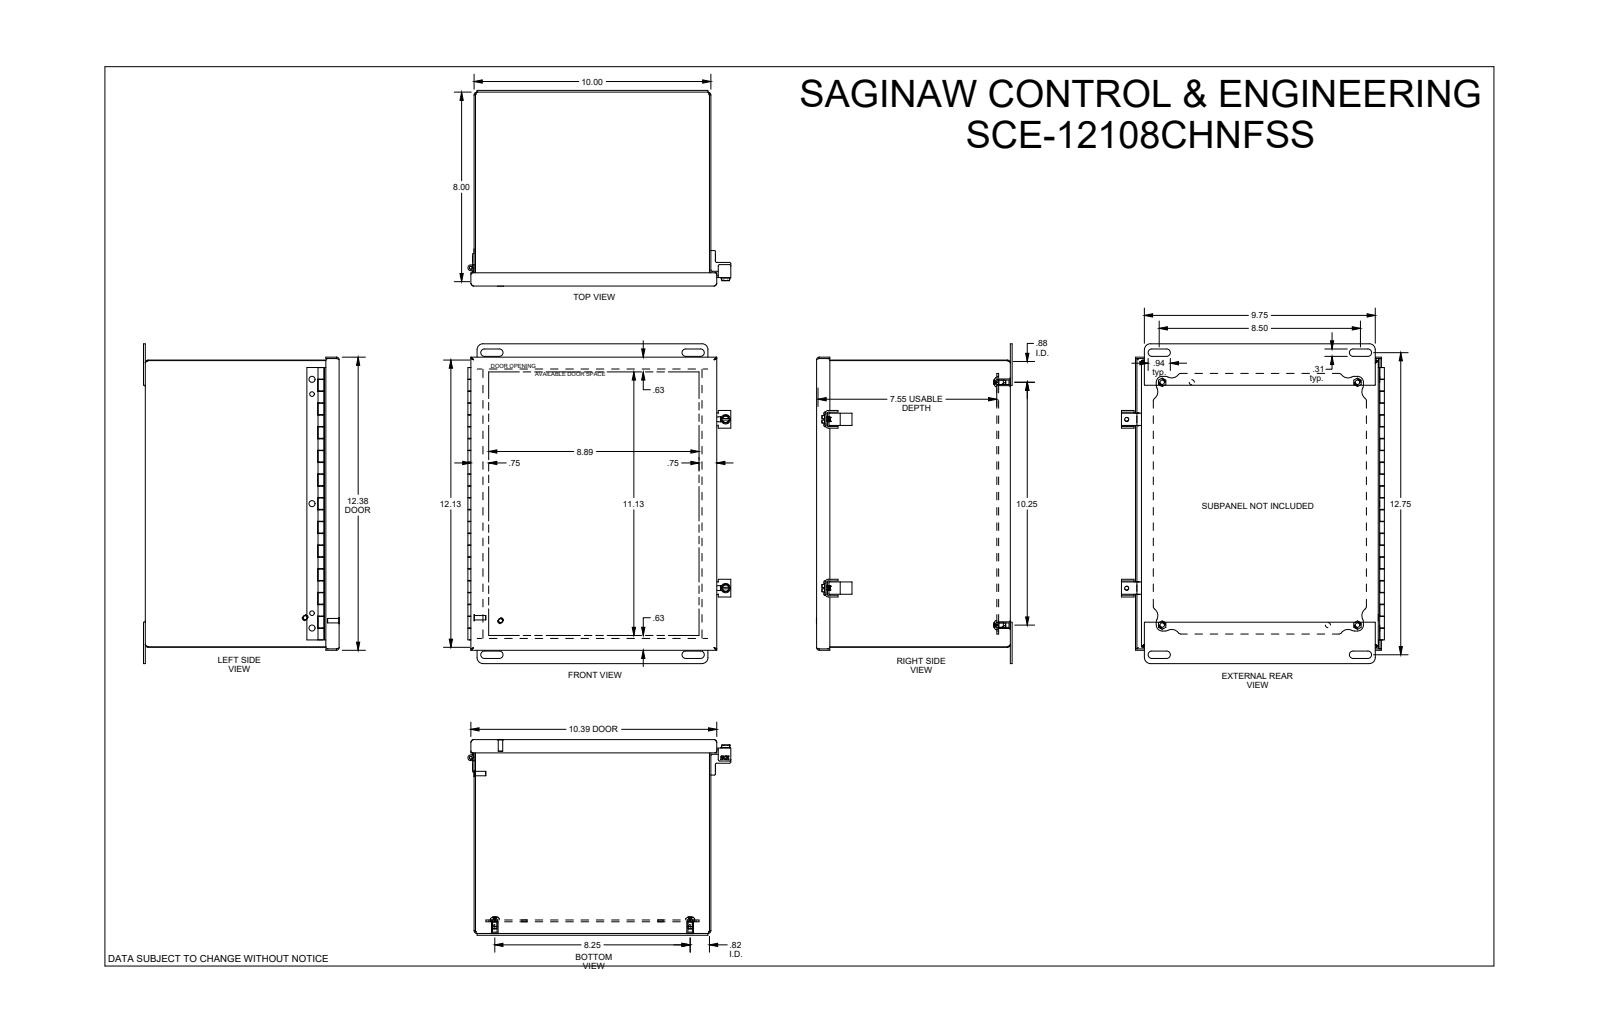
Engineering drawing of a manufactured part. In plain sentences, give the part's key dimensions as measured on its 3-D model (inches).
The part is named "SCE-12108CHNF". Its 3-D file was written by "SolidWorks 2019 (AUTOMOTIVE_DESIGN)". It is 37 solids with 1256 faces: 560 planar, 349 cylindrical and 347 other. Overall it measures 13.5 by 11.104 by 8.265 inches. Its volume is 52.55 cubic inches and its surface area 1 654 square inches. Round holes: 9 of diameter 0.19, 7 of diameter 0.193, 4 of diameter 0.25, 4 of diameter 0.281, 2 of diameter 0.156, 2 of diameter 0.218, 2 of diameter 0.266, 1 of diameter 0.126, 1 of diameter 0.187. Round bosses or shafts: 11 of diameter 0.188, 7 of diameter 0.256, 4 of diameter 0.373, 4 of diameter 0.28, 2 of diameter 0.396, 2 of diameter 0.188, 1 of diameter 0.246, 1 of diameter 0.123. Partial cylindrical surfaces (rounded edges, fillets, slot ends): 76 of radius 0.01, 33 of radius 0.06, 16 of radius 0.25, 8 of radius 0.05, 8 of radius 0.125, 8 of radius 0.156, 8 of radius 0.344, 6 of radius 0.027. The main face-to-face distances are 0.06, 8.125, 9.94, 12.065, 8.185, 8.065, 0.075, 10, 0.51, 0.435. The hole center spacings are 13.157, 10.249, 10.25, 8.25, 13.059, 9.875, 9.875, 10.326.
